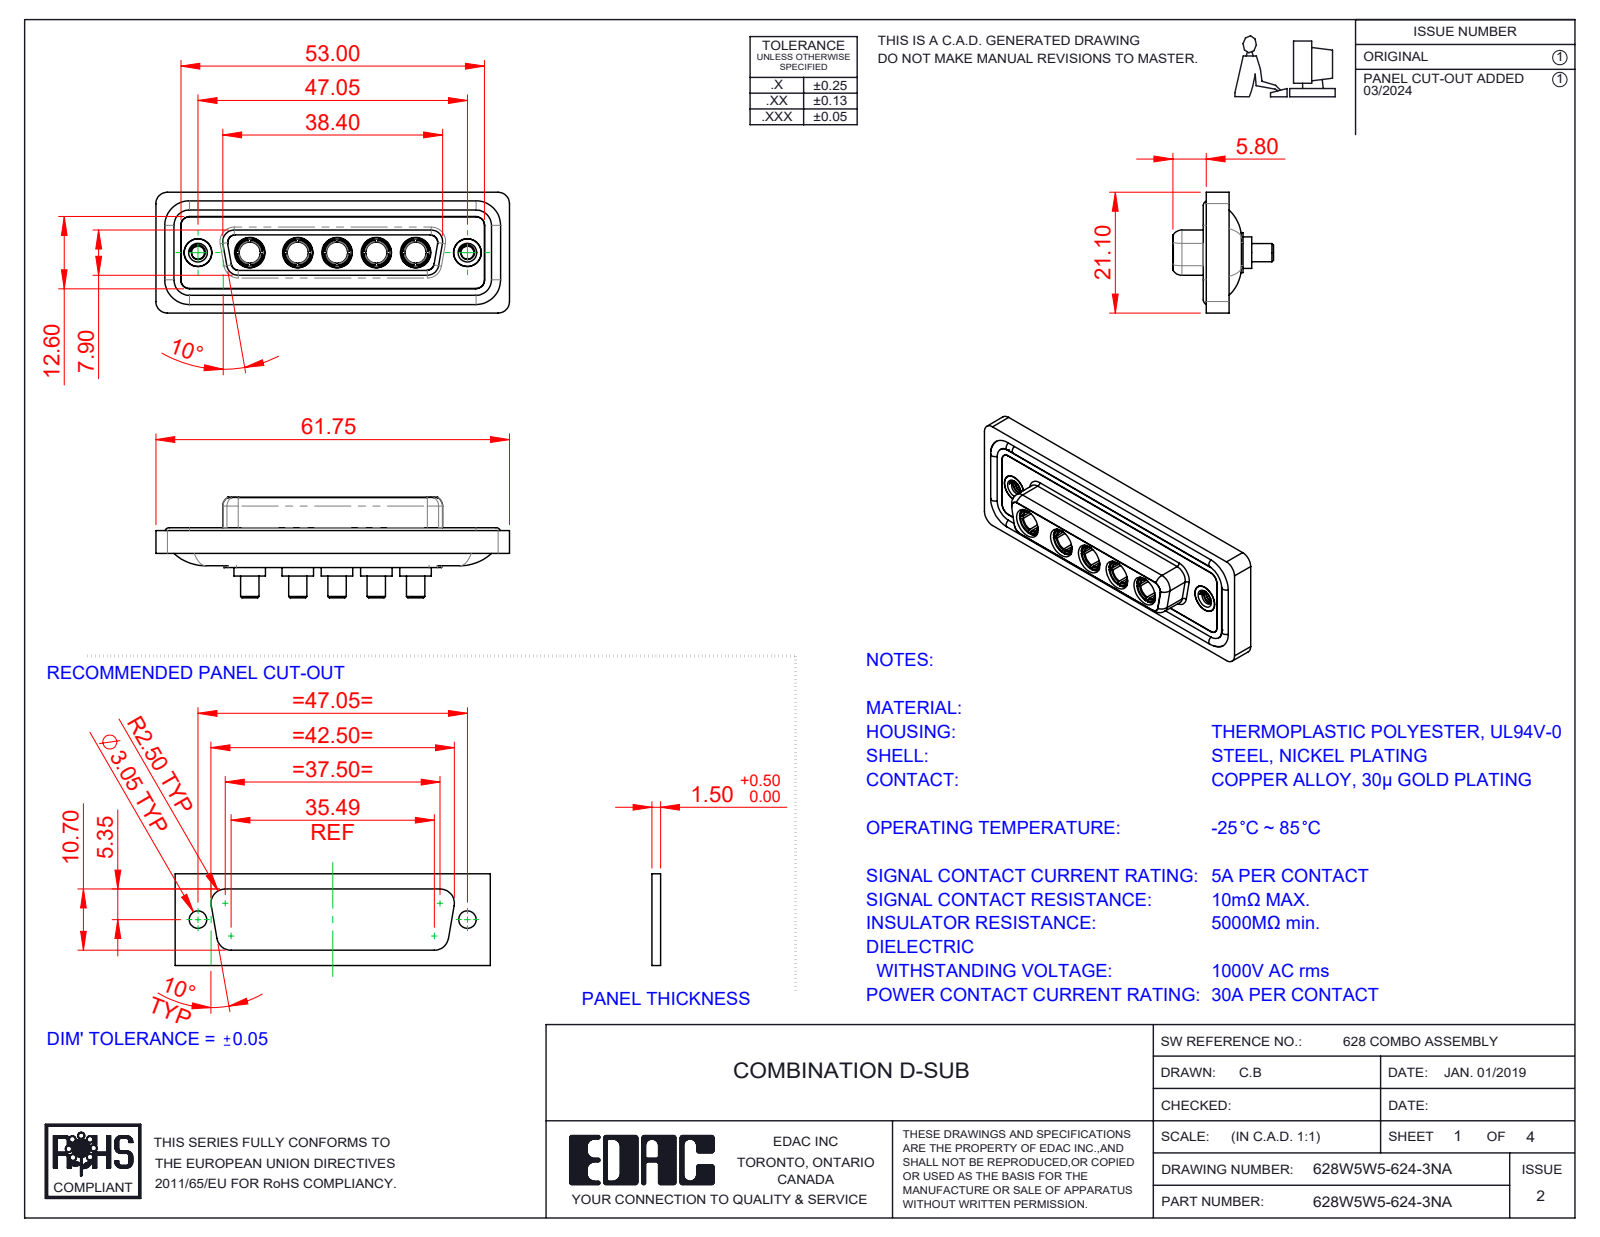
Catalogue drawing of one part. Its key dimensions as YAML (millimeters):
part_name: "628Combo Housing_5W5; 628Combo Waterproof Housing_25 Contacts; 628W5W5-624-3NA; 628Combo Threaded Rivet_A (+3 more)"
step_written_by: "SolidWorks 2023 (CONFIG_CONTROL_DESIGN)"
units: millimeters
bodies: {solids: 17, faces: 754, planar: 250, cylindrical: 305, other: 199}
overall_size: [61.75, 21.1, 17.55]
volume: 8210
surface_area: 13436
round_holes:
  - {diameter: 4.85, count: 7}
  - {diameter: 3.7, count: 5}
  - {diameter: 5.3, count: 5}
  - {diameter: 2.26, count: 2}
  - {diameter: 4, count: 2}
  - {diameter: 4.05, count: 2}
  - {diameter: 5, count: 2}
round_bosses_or_shafts:
  - {diameter: 5.5, count: 5}
  - {diameter: 5.2, count: 5}
  - {diameter: 4.96, count: 5}
  - {diameter: 4.75, count: 5}
  - {diameter: 3.75, count: 5}
  - {diameter: 3.2, count: 5}
  - {diameter: 1.6, count: 4}
  - {diameter: 4.95, count: 2}
partial_cylinders:
  - {radius: 1.5, count: 22}
  - {radius: 2, count: 18}
  - {radius: 1.35, count: 8}
  - {radius: 1.6, count: 8}
  - {radius: 2.1, count: 5}
  - {radius: 0.25, count: 4}
  - {radius: 0.5, count: 4}
  - {radius: 0.6, count: 4}
face_to_face_distances: [0.4, 1.8, 7.45, 5.65, 0.5, 7.05, 6.6, 1.6, 1.1, 2.9]
hole_center_spacings: [6.86, 9.04, 13.72, 38.01, 8.39, 15.25, 15.9, 17.43]
